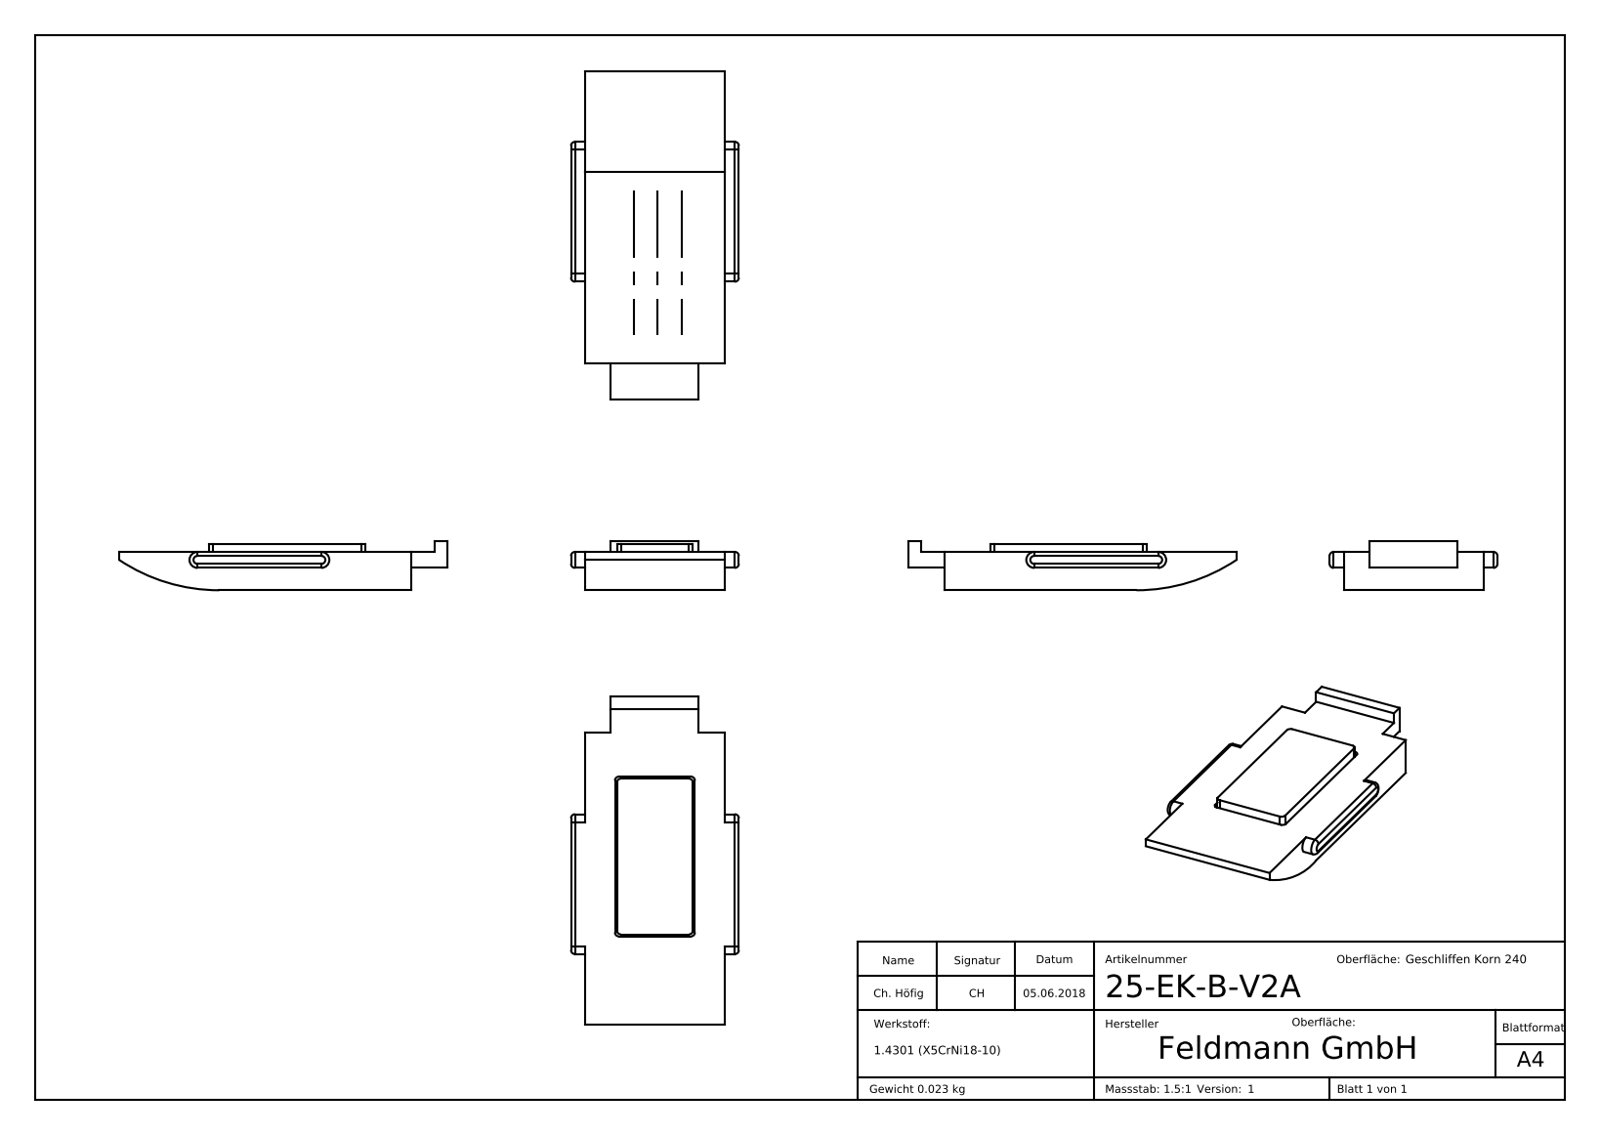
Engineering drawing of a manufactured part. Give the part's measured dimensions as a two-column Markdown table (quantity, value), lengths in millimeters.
| quantity | value |
| --- | --- |
| part name | 25-EK-B-V2A; 25-EK-B-XXX Teil1_25-EK-B-V2A Teil1; 25-EK-B-XXX Teil2_25-EK-B-XXX Teil2 |
| STEP written by | SolidWorks 2015 (CONFIG_CONTROL_DESIGN) |
| units | millimeters |
| bodies | 2 solids, 235 faces (154 planar, 19 cylindrical, 62 other) |
| overall size | 41.01 × 21 × 6.2 |
| volume | 3 206 mm³ |
| surface area | 2 532 mm² |
| partial cylindrical surfaces (radius × count) | 0.5 × 12, 1 × 2, 22.5 × 1 |
| main face-to-face distances | 1, 4.8, 3.8, 2, 5.8, 17.5, 3, 2.8, 4, 13.5 |
